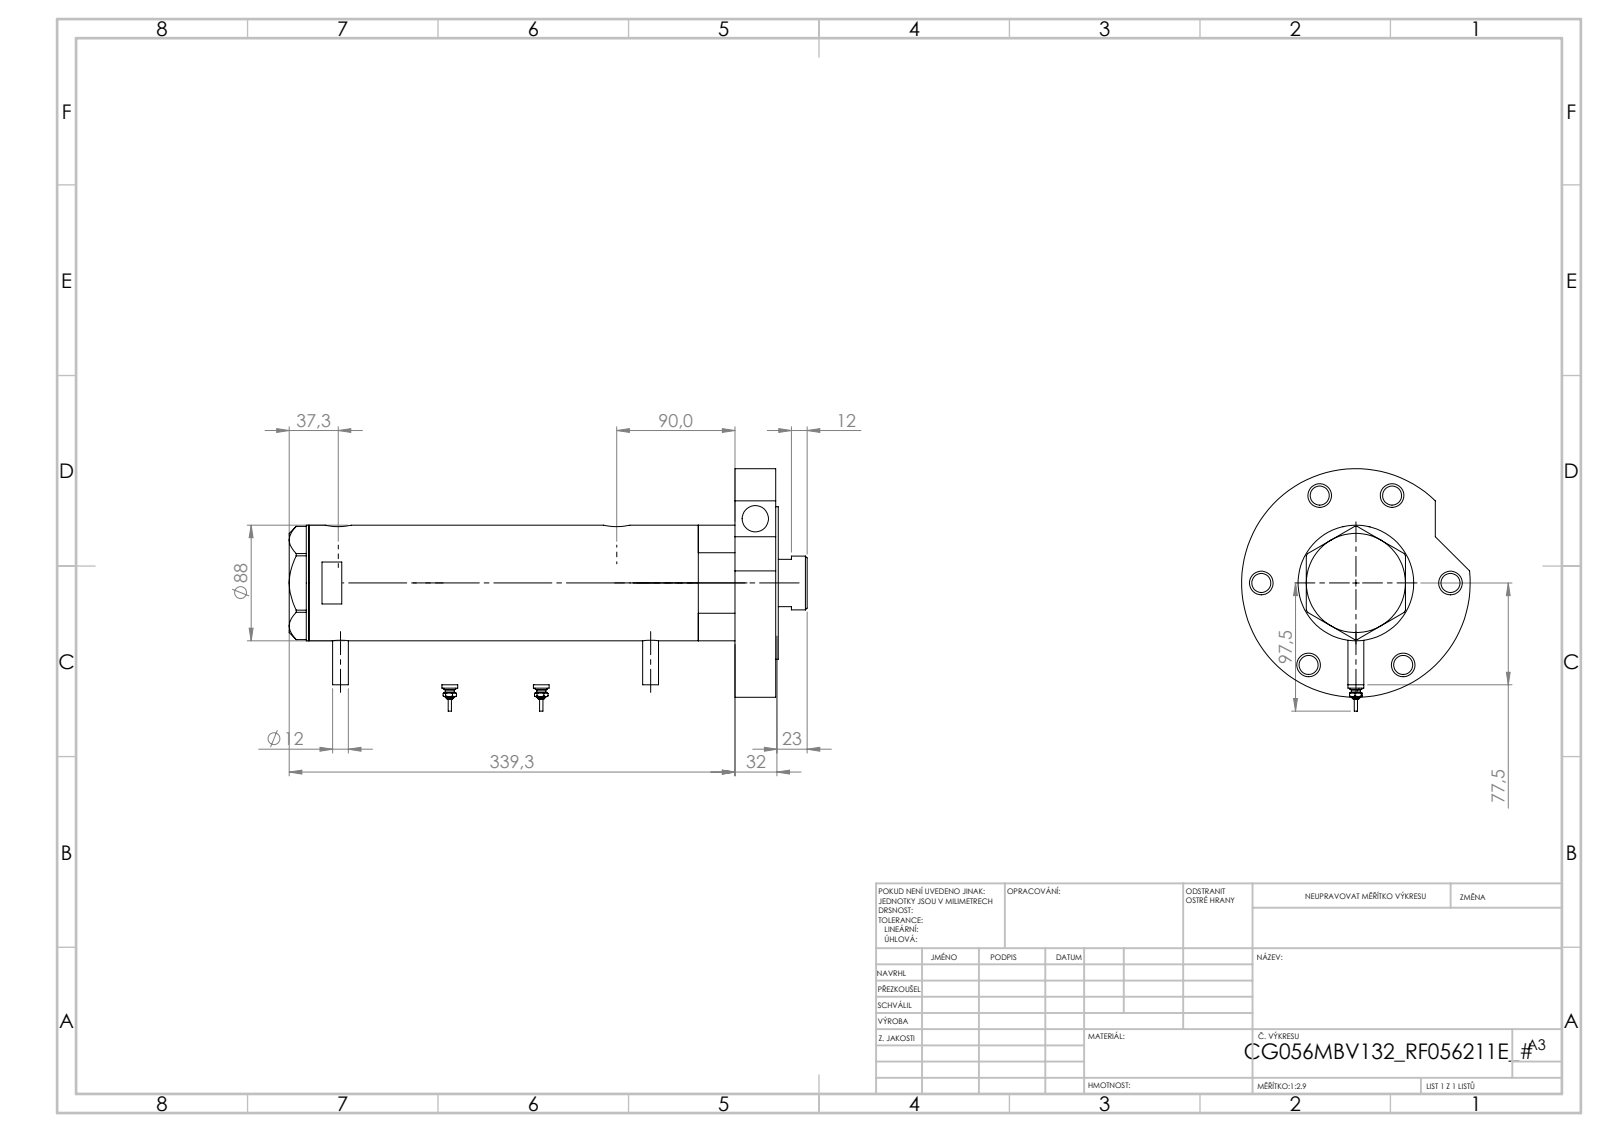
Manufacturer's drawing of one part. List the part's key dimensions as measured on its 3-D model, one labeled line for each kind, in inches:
Part name (STEP PRODUCT): V270CG_BACK; V270CG_FRONT; V270CG_RF211E; V270CG_VC (+2 more)
STEP written by: SolidWorks 2019 (CONFIG_CONTROL_DESIGN)
Units: inches
Bodies: 7 solids, 257 faces (91 planar, 102 cylindrical, 64 other)
Overall size (bounding box): 15.524 × 7.264 × 6.85
Volume: 157.4 in³ · Surface area: 560.3 in²
Round holes (diameter × count): ⌀0.571 ×7, ⌀0.709 ×6, ⌀0.787 ×3, ⌀0.492 ×2, ⌀0.518 ×2, ⌀1.654 ×1, ⌀1.713 ×1, ⌀2.205 ×1, ⌀2.362 ×1, ⌀2.953 ×1, ⌀3.15 ×1
Round bosses / shafts (diameter × count): ⌀0.472 ×4, ⌀0.354 ×2, ⌀0.276 ×2, ⌀0.177 ×2, ⌀0.098 ×2, ⌀6.85 ×1, ⌀4.567 ×1, ⌀3.465 ×1
Main face-to-face distances: 1.22, 0.079, 14.067, 12.768, 13.988, 1.299, 9.228, 3.539, 4.76, 4.839
Hole centre spacings: 2.835, 3.15, 4.714, 4.91, 5.085, 5.657, 0.067, 1.016
